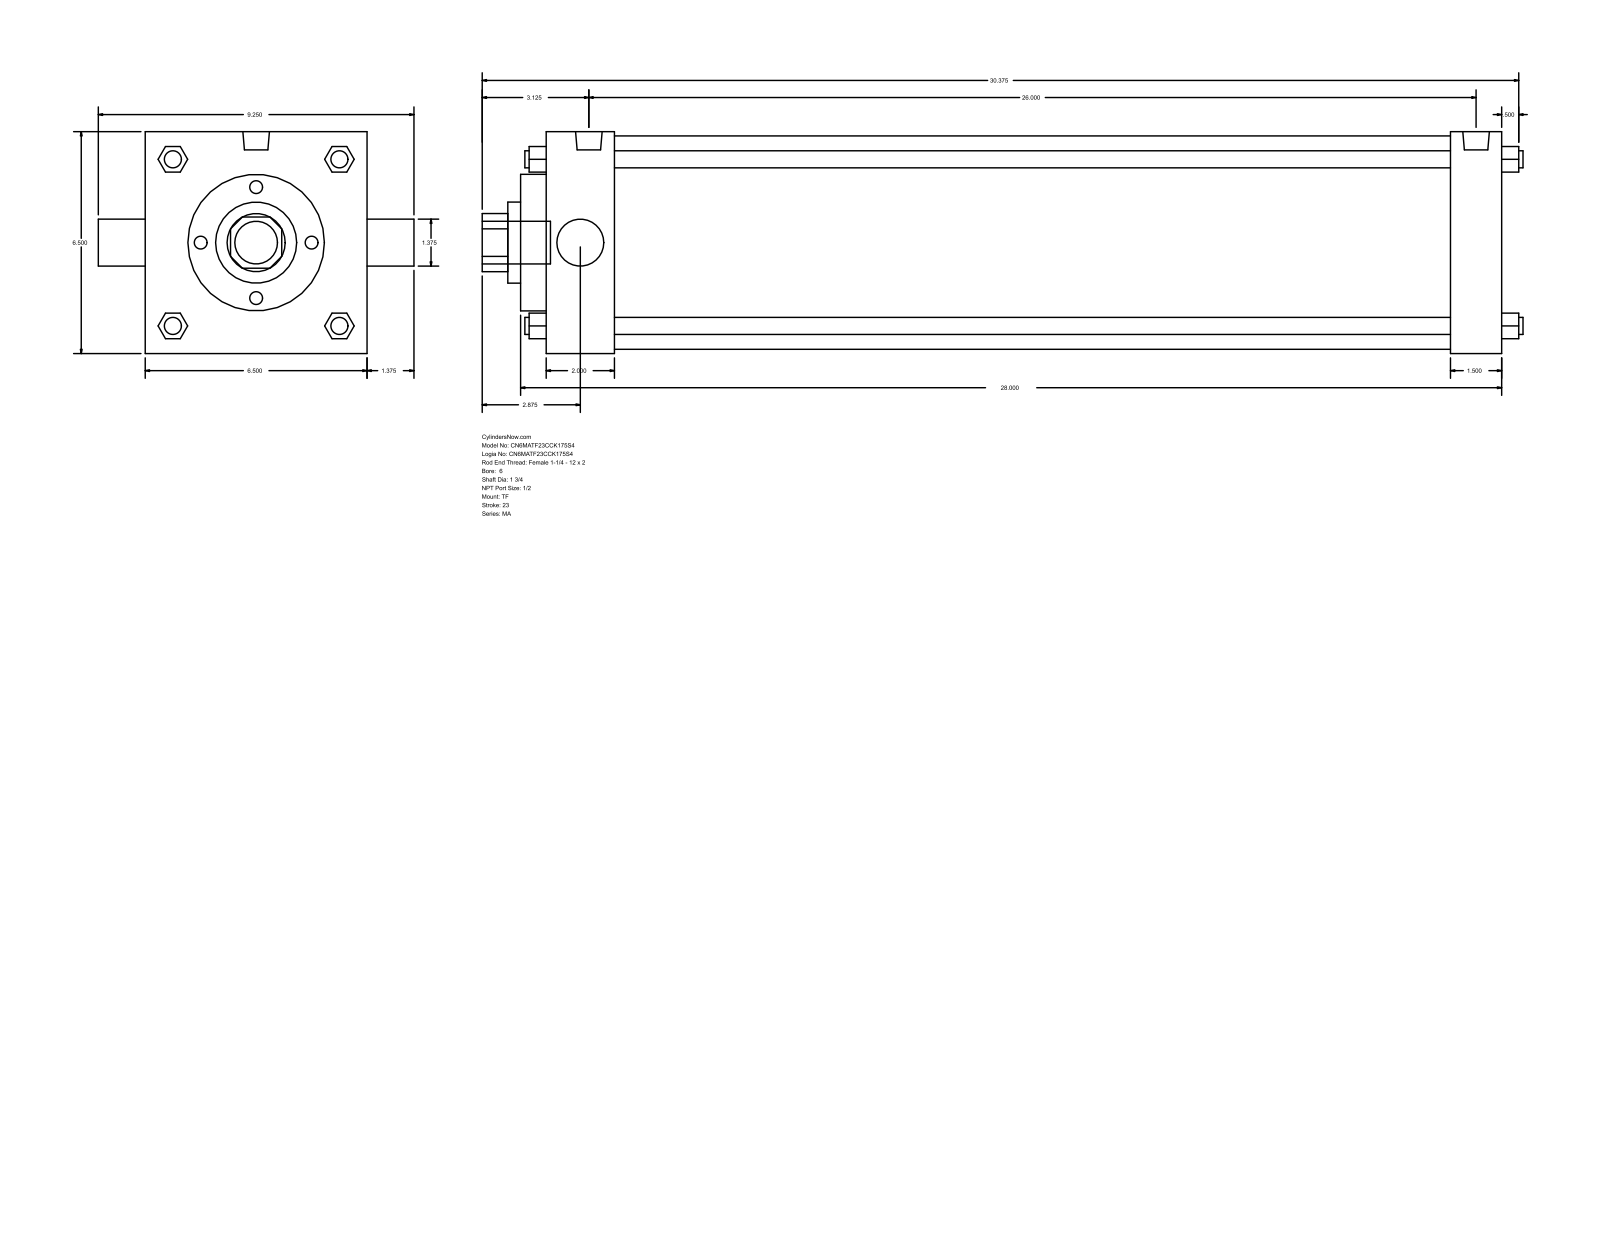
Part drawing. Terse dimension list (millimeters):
name: MA_TF__0600_1.75
written by: GSSL Pune (CONFIG_CONTROL_DESIGN)
unit: mm
bodies: 0 solids, 122 faces (93 planar, 29 cylindrical, 0 other)
size: 774.7 × 234.95 × 165.1
holes: 1× ⌀34.92, 1× ⌀44.45, 1× ⌀60.33, 1× ⌀101.6, 1× ⌀158.75
bosses: 4× ⌀12.7, 3× ⌀17.46, 2× ⌀19.77, 1× ⌀31.75
rounds: 1× R21.63
face distances: 165.1, 711.21, 19.05, 38.1, 50.8, 660.41, 673.11, 622.31, 69.85, 692.16
